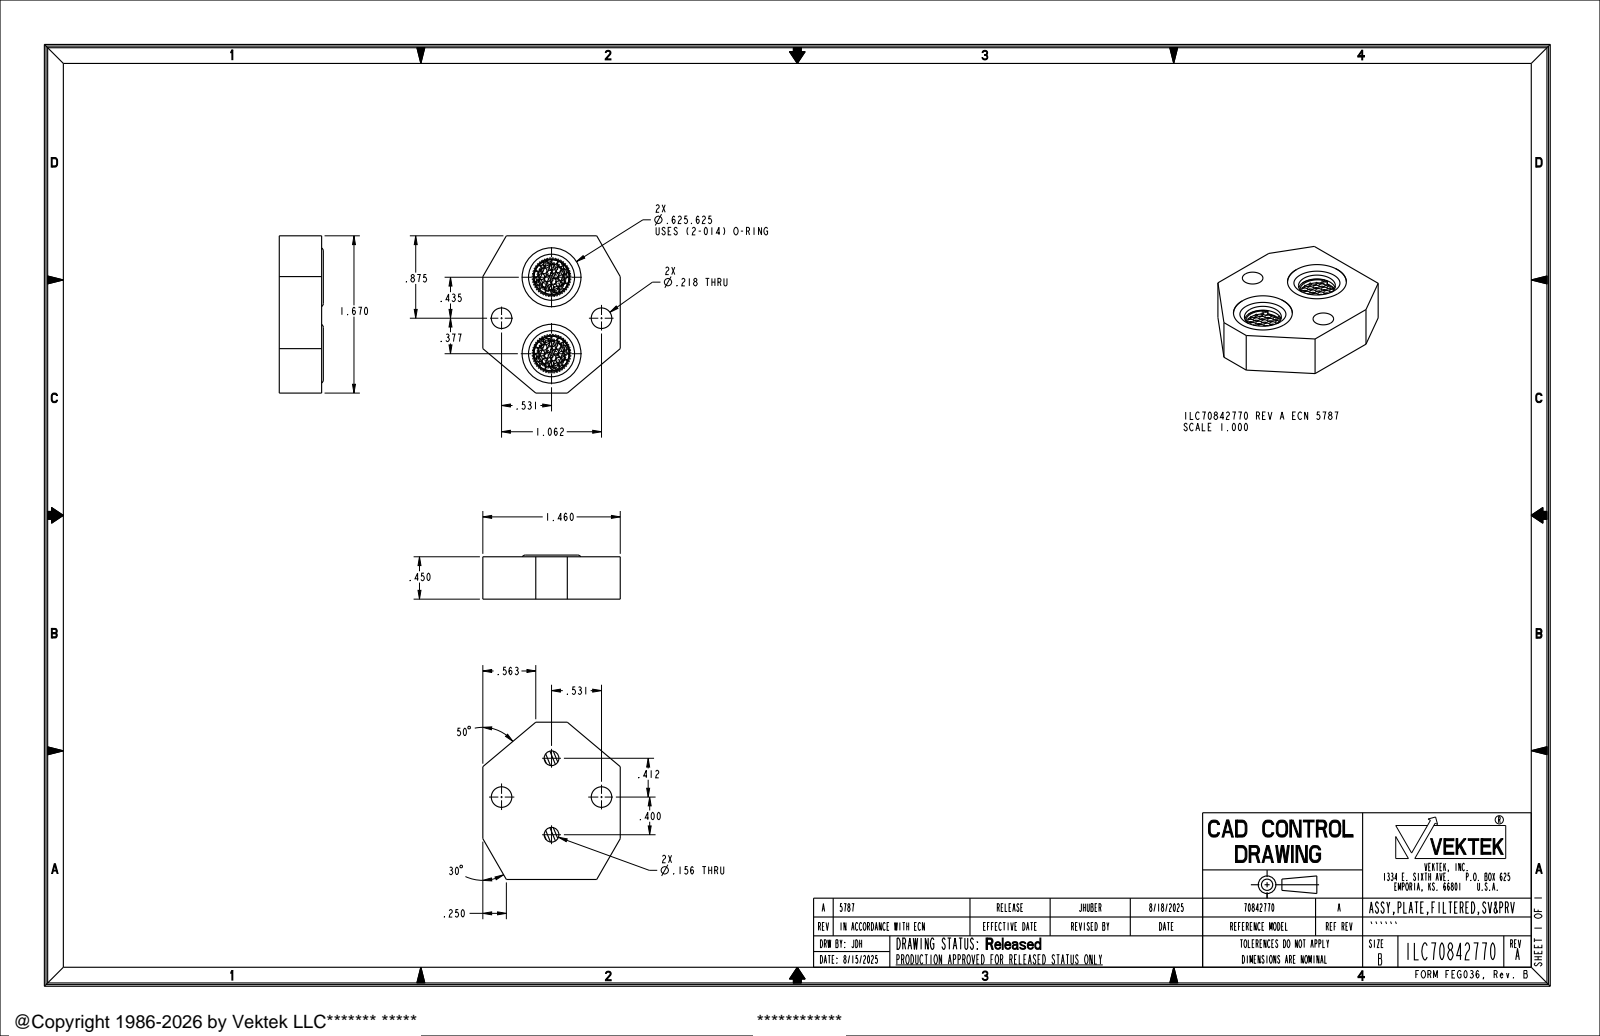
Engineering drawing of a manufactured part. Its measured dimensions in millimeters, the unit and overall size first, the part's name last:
Units: millimetres
Overall size (bounding box): 42.4 × 37.1 × 11.9
Round holes (diameter × count): ⌀1.6 ×32, ⌀4 ×2, ⌀5.5 ×2, ⌀6.7 ×2, ⌀7.4 ×2, ⌀8 ×2, ⌀10 ×2, ⌀10.4 ×2, ⌀15.9 ×2
Round bosses / shafts (diameter × count): ⌀9.5 ×2, ⌀9.4 ×2
Partial cylindrical surfaces — rounded edges, fillets, slot ends (radius × count): R0.8 ×32, R0.5 ×14, R0.4 ×8, R0.7 ×6, R0.3 ×4, R0.4 ×4, R0.6 ×4, R3.8 ×2
Main face-to-face distances: 11.4, 10.1, 1.3, 37.1, 3.3, 1.3, 2.5, 42.4, 8.8, 7.9
Hole centre spacings: 1.7, 3.4, 3.8, 2.4, 2.7, 3.8, 5.3, 5.1
Volume: 13 200 mm³ · Surface area: 6 787 mm²
Bodies: 1 solid, 482 faces (178 planar, 300 cylindrical, 4 other)
Part name (STEP PRODUCT): ILC70842770
STEP written by: CREO PARAMETRIC BY PTC INC, 2021164 (AUTOMOTIVE_DESIGN)
